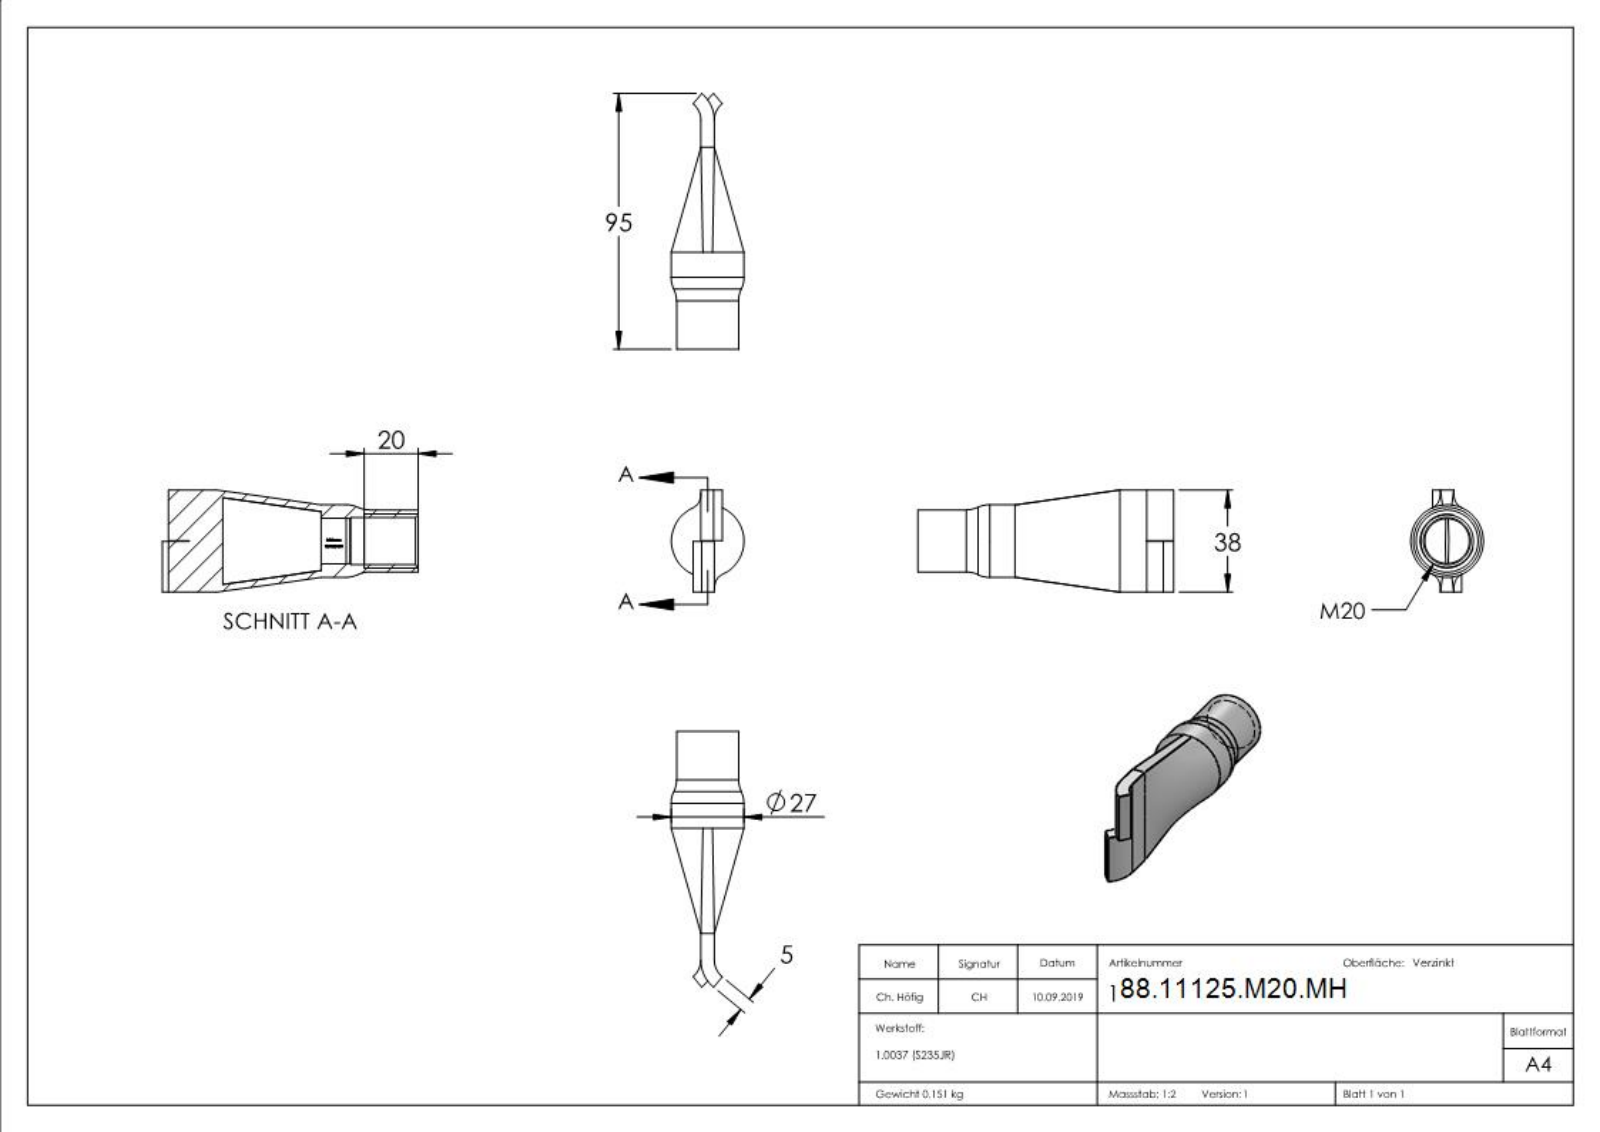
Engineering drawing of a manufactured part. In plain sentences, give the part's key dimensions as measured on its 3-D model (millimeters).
The part is named "125-M20-MH". Its 3-D file was written by "SolidWorks 2015 (CONFIG_CONTROL_DESIGN)". It is 1 solid with 279 faces: 136 planar, 48 cylindrical and 95 other. Overall it measures 95 by 38 by 27 millimeters. Its volume is 19 405 cubic millimeters and its surface area 12 628 square millimeters. Round holes: 1 of diameter 17, 1 of diameter 17.5. Round bosses or shafts: 1 of diameter 27, 1 of diameter 23, 1 of diameter 22. Partial cylindrical surfaces (rounded edges, fillets, slot ends): 2 of radius 7.93, 2 of radius 12.93, 1 of radius 8.6. The main face-to-face distances are 5, 36, 38, 18.95, 19.05, 72.5, 36.5, 85, 49, 12.5.
